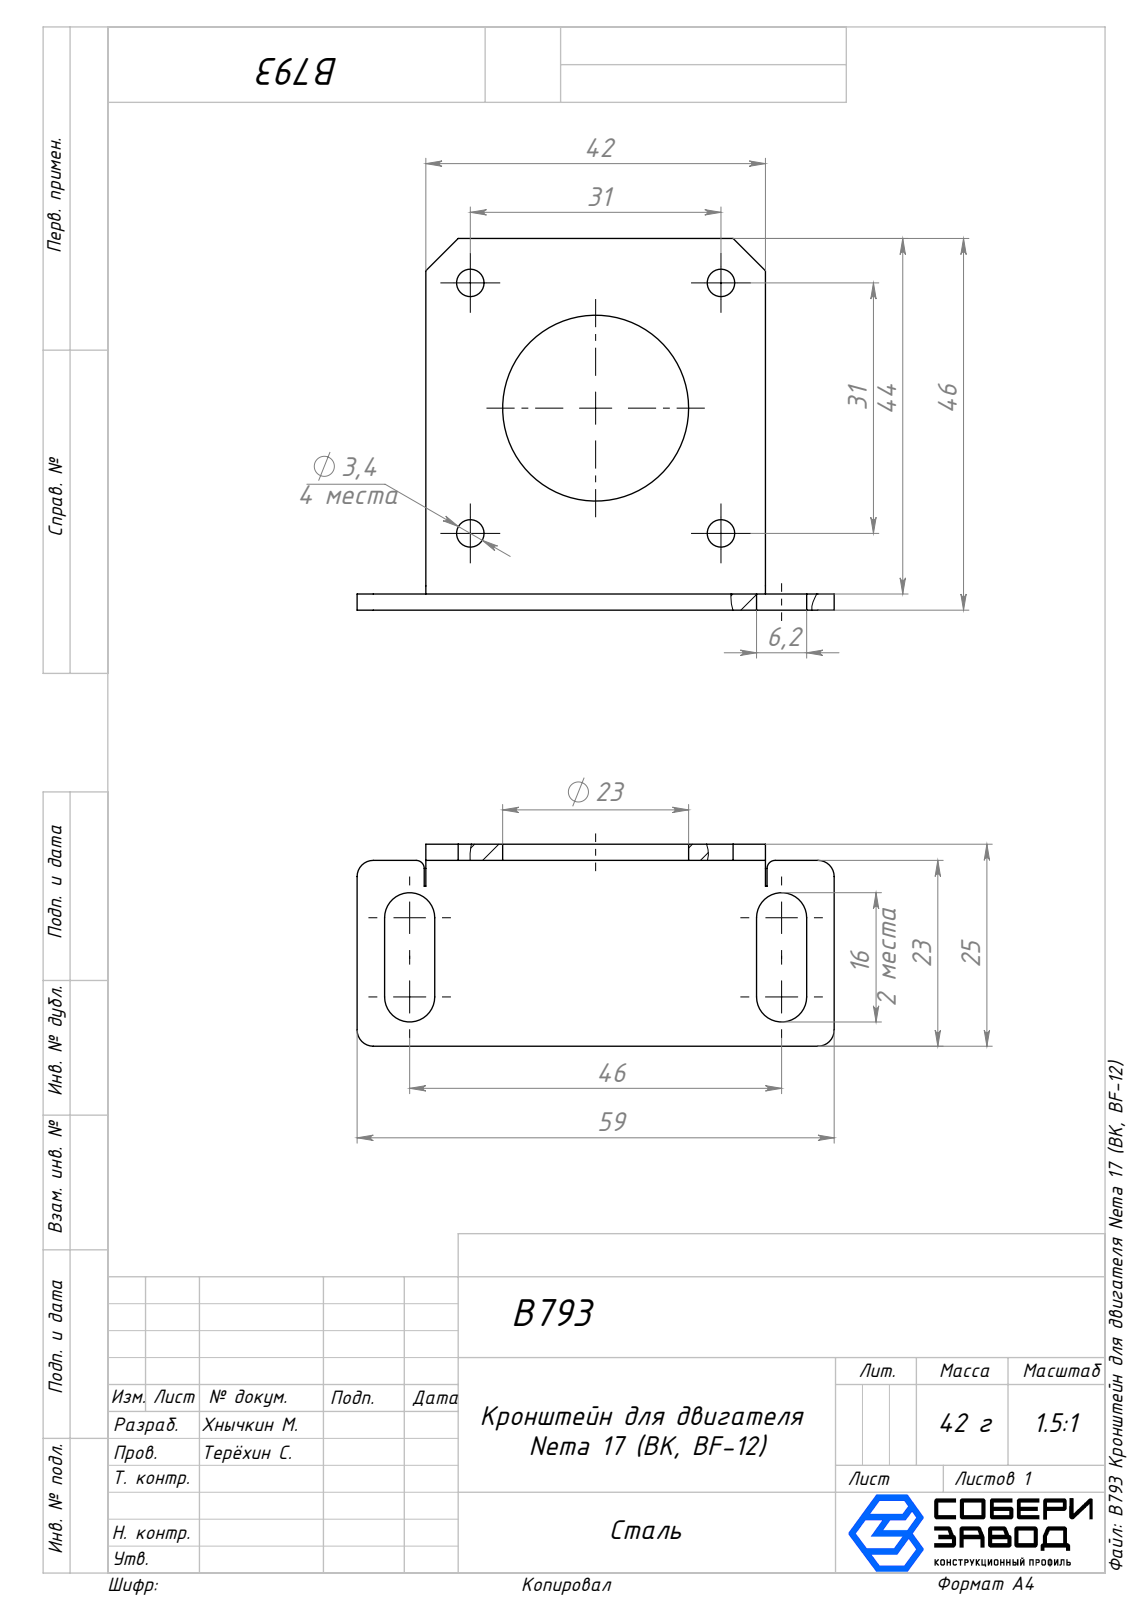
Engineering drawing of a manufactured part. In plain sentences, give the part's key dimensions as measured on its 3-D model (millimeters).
The part is named "B793 Кронштейн для двигателя Nema 17 (BK, BF-12)". Its 3-D file was written by "SolidWorks 2025 (AUTOMOTIVE_DESIGN)". It is 1 solid with 48 faces: 26 planar, 22 cylindrical and 0 other. Overall it measures 59 by 46 by 25 millimeters. Its volume is 5 196 cubic millimeters and its surface area 6 099 square millimeters. Round holes: 4 of diameter 3.4, 1 of diameter 23. Partial cylindrical surfaces (rounded edges, fillets, slot ends): 4 of radius 2, 4 of radius 3.1, 3 of radius 1, 1 of radius 3. The main face-to-face distances are 2, 25, 23, 46, 42, 8.5, 50.5, 44, 3.4, 9.6. The hole center spacings are 21.92, 31, 43.84.
